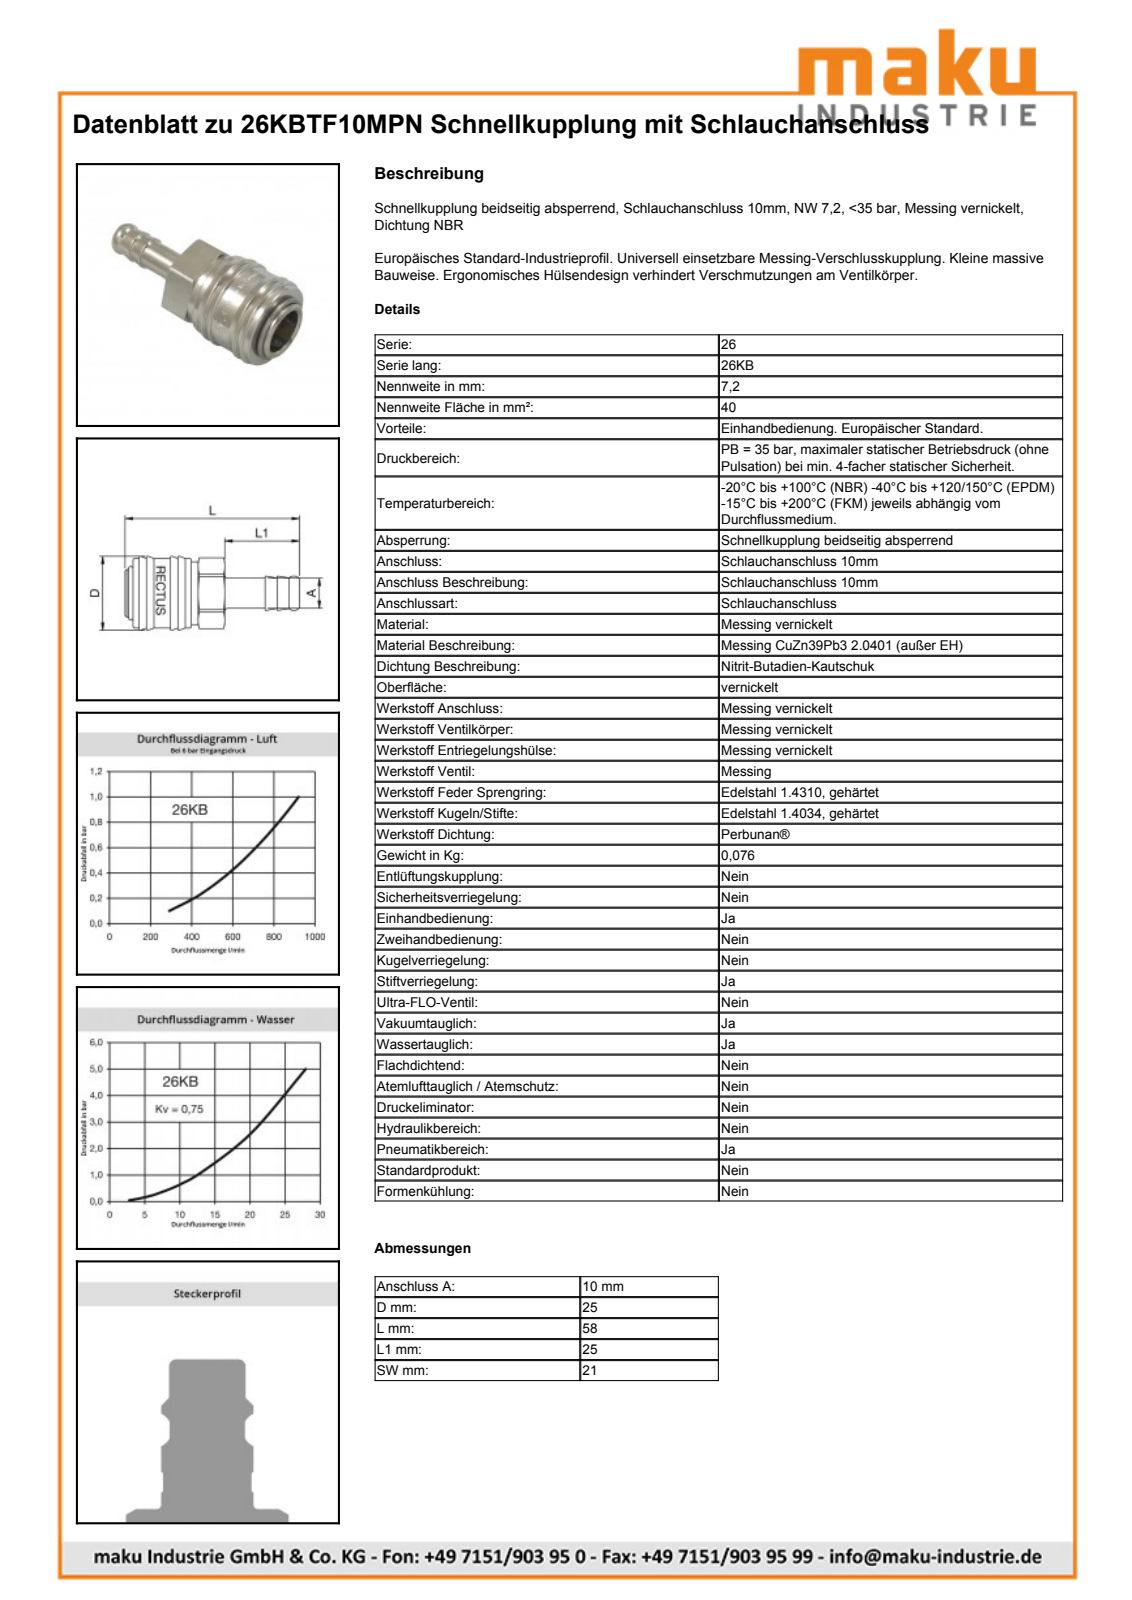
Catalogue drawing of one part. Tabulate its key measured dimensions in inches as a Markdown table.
| quantity | value |
| --- | --- |
| part name | D106706 |
| STEP written by | Autodesk Inventor 2011 (AUTOMOTIVE_DESIGN) |
| units | inches |
| bodies | 2 solids, 462 faces (175 planar, 59 cylindrical, 228 other) |
| overall size | 2.283 × 0.976 × 0.976 |
| volume | 0.818 in³ |
| surface area | 11.52 in² |
| round holes (diameter × count) | 0.634 × 1, 0.669 × 1, 0.831 × 1 |
| round bosses / shafts (diameter × count) | 0.917 × 1, 0.827 × 1, 0.709 × 1, 0.656 × 1, 0.628 × 1, 0.589 × 1, 0.398 × 1 |
| partial cylindrical surfaces (radius × count) | 0.305 × 1, 0.455 × 1, 0.467 × 1 |
| main face-to-face distances | 0.827, 1.195, 0.104, 1.299, 0.826, 0.828, 0.722, 0.472, 2.283, 2.179 |
